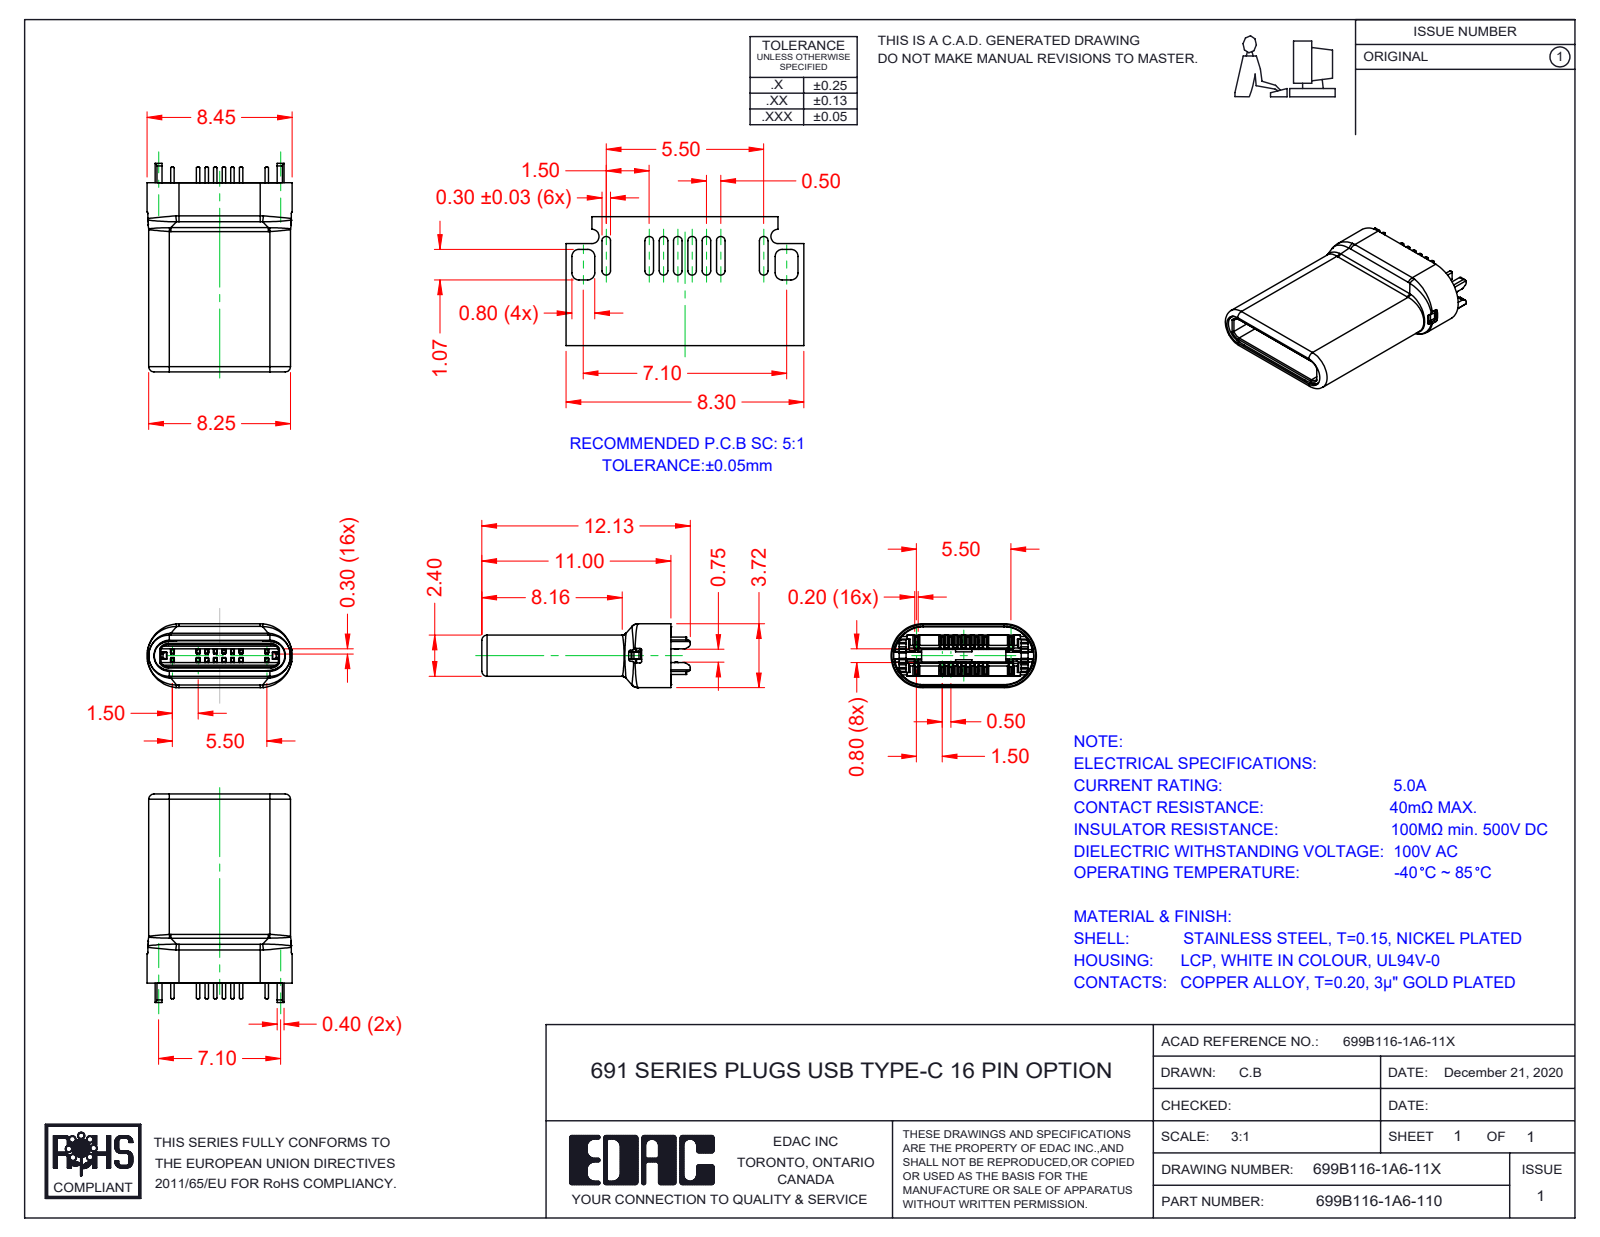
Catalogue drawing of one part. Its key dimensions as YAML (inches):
part_name: "Insulator 699B116-1A6-11X_White; 699B116-1A6-110; Shell 699B116-1A6-11X; Contacts 699B116-1A6-11X"
step_written_by: "SolidWorks 2020 (AUTOMOTIVE_DESIGN)"
units: inches
bodies: {solids: 19, faces: 1586, planar: 985, cylindrical: 498, other: 103}
overall_size: [0.478, 0.333, 0.146]
volume: 0.01
surface_area: 1.934
partial_cylinders:
  - {radius: 0.008, count: 30}
  - {radius: 0.006, count: 28}
  - {radius: 0.004, count: 20}
  - {radius: 0.012, count: 14}
  - {radius: 0.005, count: 8}
  - {radius: 0.02, count: 8}
  - {radius: 0.018, count: 4}
  - {radius: 0.039, count: 4}
face_to_face_distances: [0.059, 0.02, 0.039, 0.089, 0.088, 0.082, 0.098, 0.079, 0.081, 0.028]
